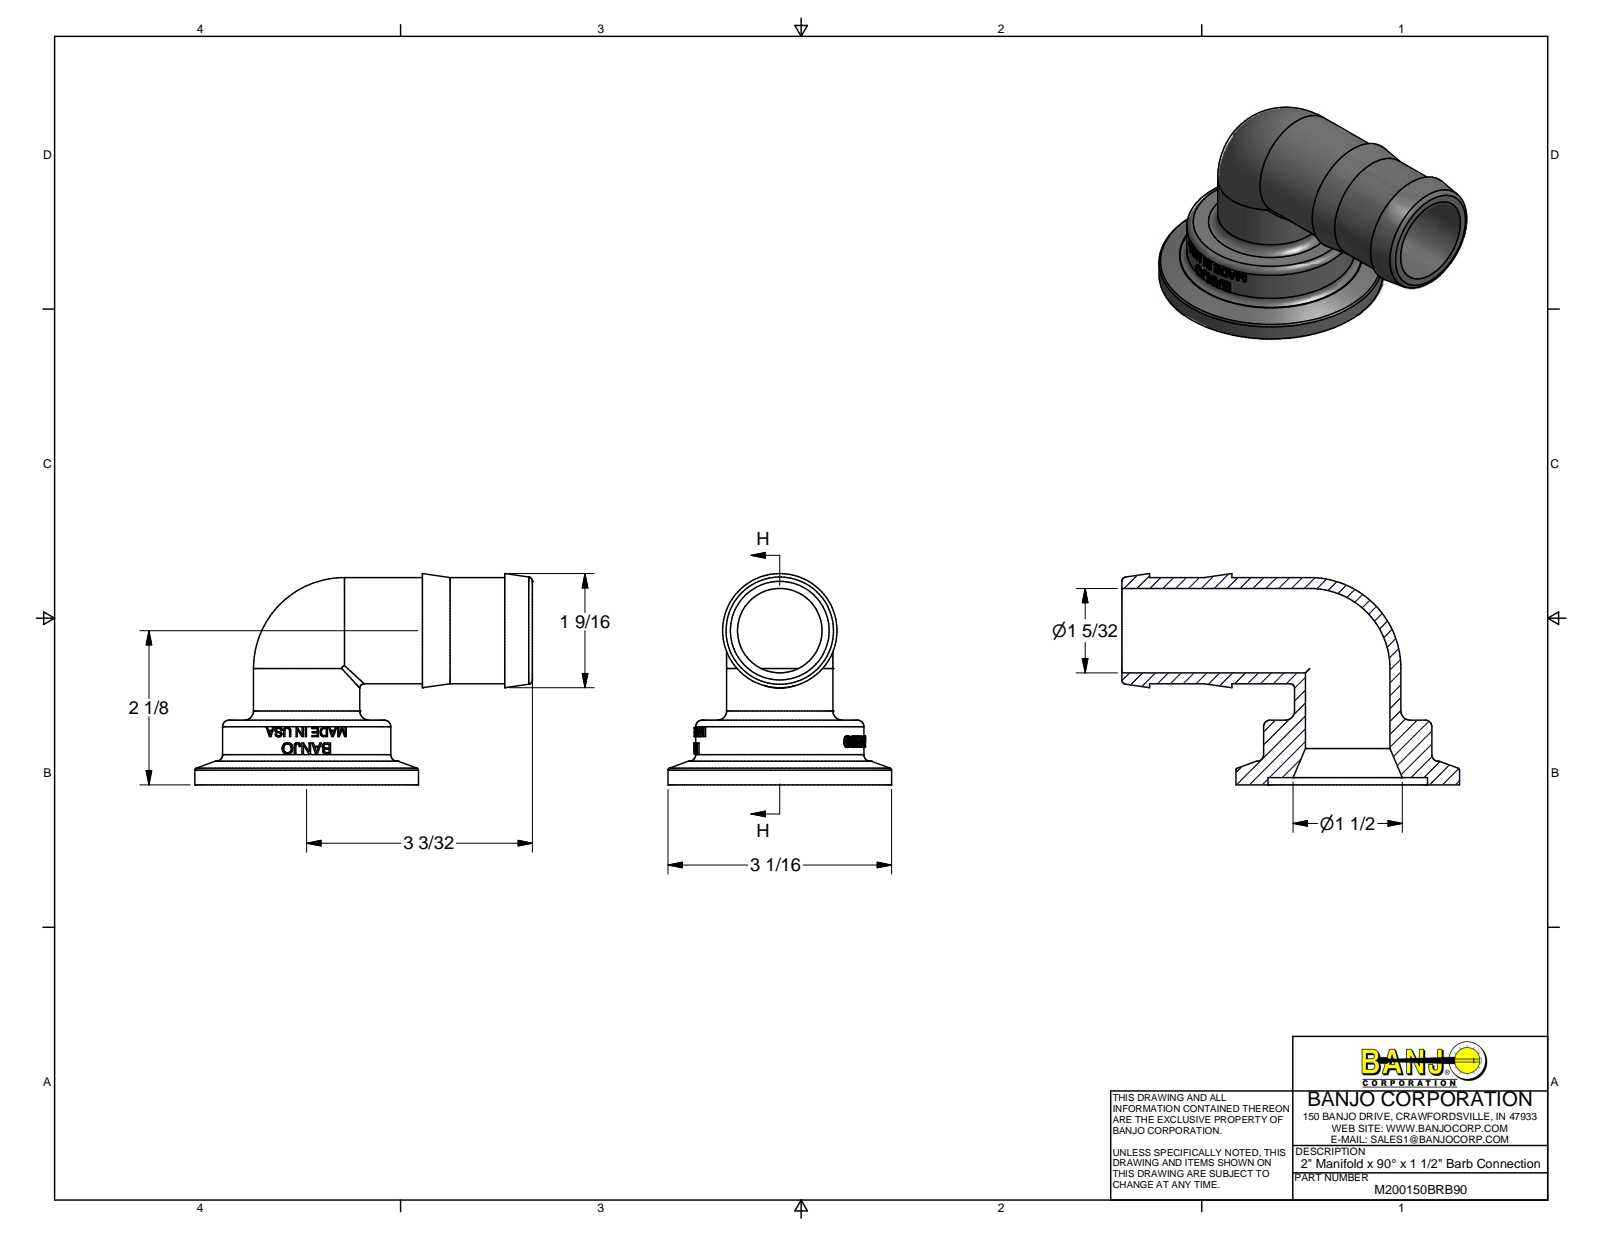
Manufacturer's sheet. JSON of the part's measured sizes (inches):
{"part_name": "M200150BRB90", "step_written_by": "Autodesk Inventor 2013 (AUTOMOTIVE_DESIGN)", "units": "inches", "bodies": {"solids": 1, "faces": 442, "planar": 193, "cylindrical": 52, "other": 197}, "overall_size": [4.635, 3.07, 2.905], "volume_in3": 5.937, "surface_area_in2": 56.19, "round_holes": [[1.16, 2], [2.19, 1]], "round_bosses_or_shafts": [[1.46, 2], [3.07, 1], [2.31, 1]], "partial_cylinders_radius": [[1.175, 1]], "face_to_face_distances": [0.1, 0.79, 0.89, 0.38, 1.51, 1.13, 0.566, 0.224, 0.324, 0.15]}
